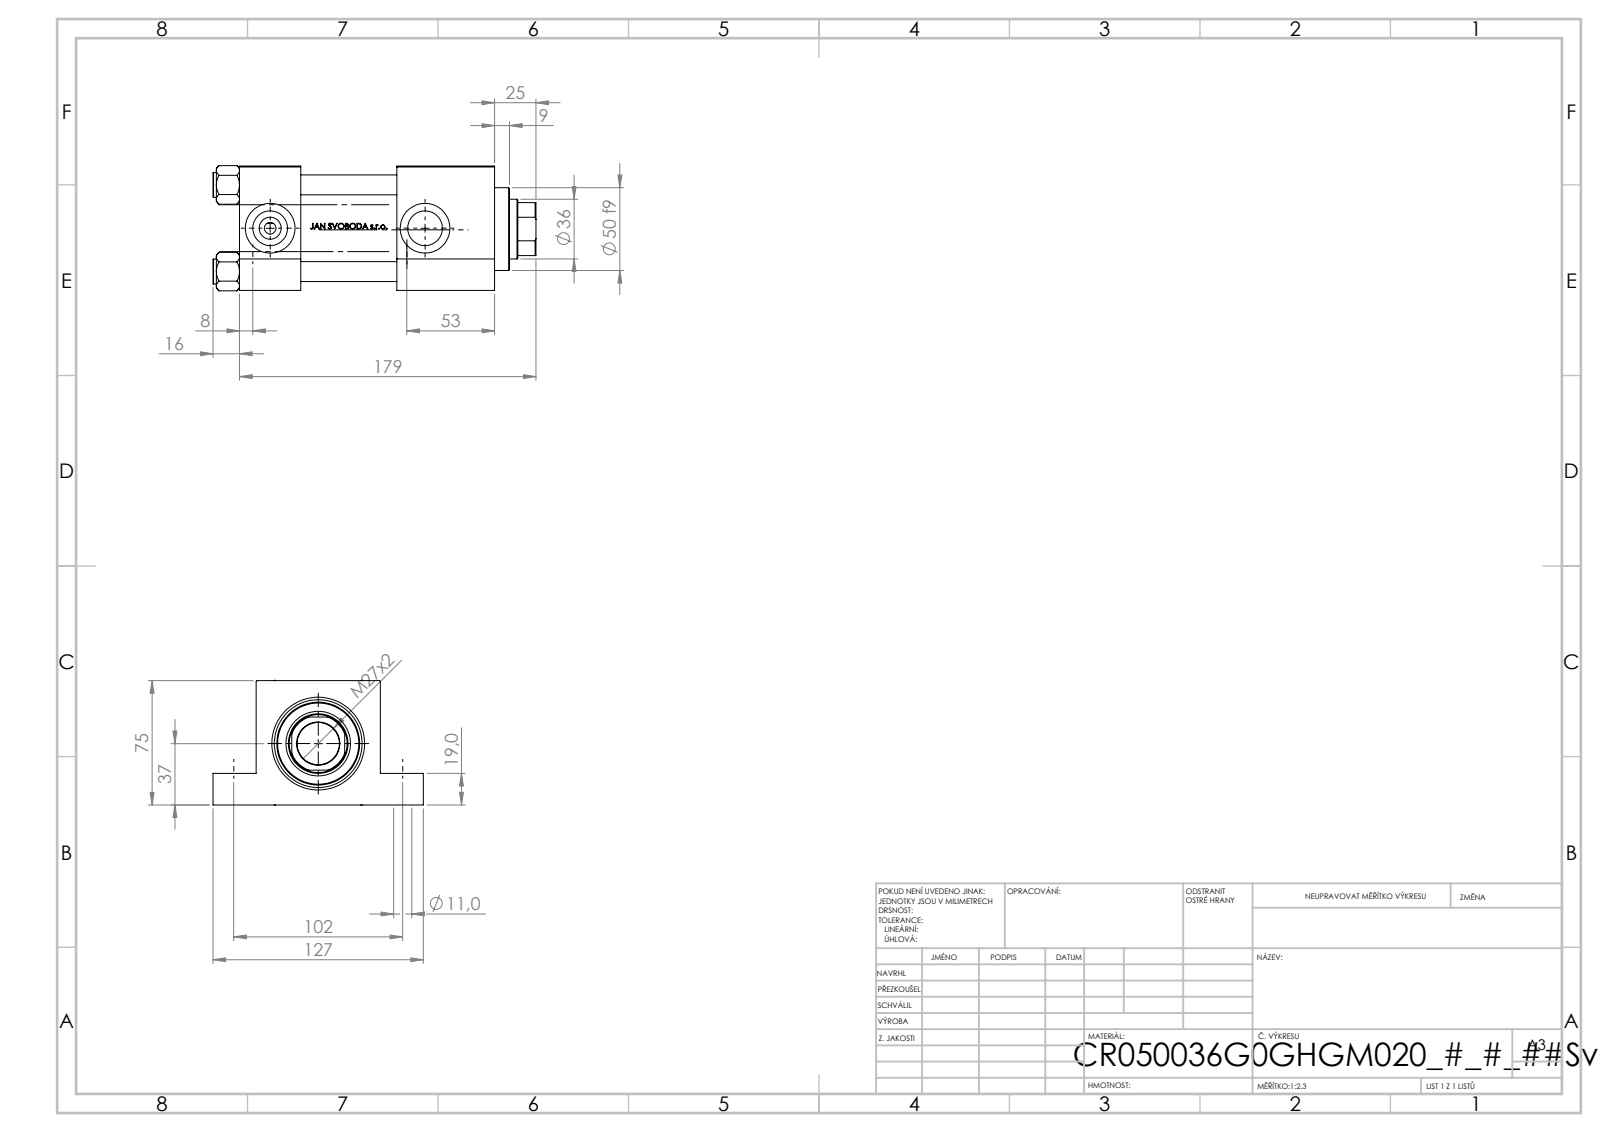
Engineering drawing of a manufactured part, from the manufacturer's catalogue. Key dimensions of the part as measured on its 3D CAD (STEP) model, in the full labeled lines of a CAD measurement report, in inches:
Part name (STEP PRODUCT): V215CR_G_TYCINKA; V215CR_G_Body; NUT_M5_G; V215_VC_A (+1 more)
STEP written by: SolidWorks 2019 (CONFIG_CONTROL_DESIGN)
Units: inches
Bodies: 11 solids, 1087 faces (431 planar, 124 cylindrical, 532 other)
Overall size (bounding box): 7.677 × 5 × 2.974
Volume: 47.9 in³ · Surface area: 259.7 in²
Round holes (diameter × count): ⌀0.472 ×4, ⌀0.433 ×3, ⌀0.276 ×2, ⌀0.825 ×2, ⌀1.181 ×2, ⌀0.433 ×1, ⌀1.004 ×1, ⌀1.417 ×1, ⌀1.535 ×1, ⌀1.614 ×1, ⌀2.087 ×1
Round bosses / shafts (diameter × count): ⌀0.591 ×4, ⌀2.205 ×1, ⌀1.969 ×1
Partial cylindrical surfaces — rounded edges, fillets, slot ends (radius × count): R0.689 ×1
Main face-to-face distances: 2.953, 1.457, 0.748, 2.205, 6.063, 4.606, 3.74, 2.283, 2.323, 1.024
Hole centre spacings: 2.059, 1.442, 1.47, 2.912, 4.016, 4.409, 5.964, 3.681
